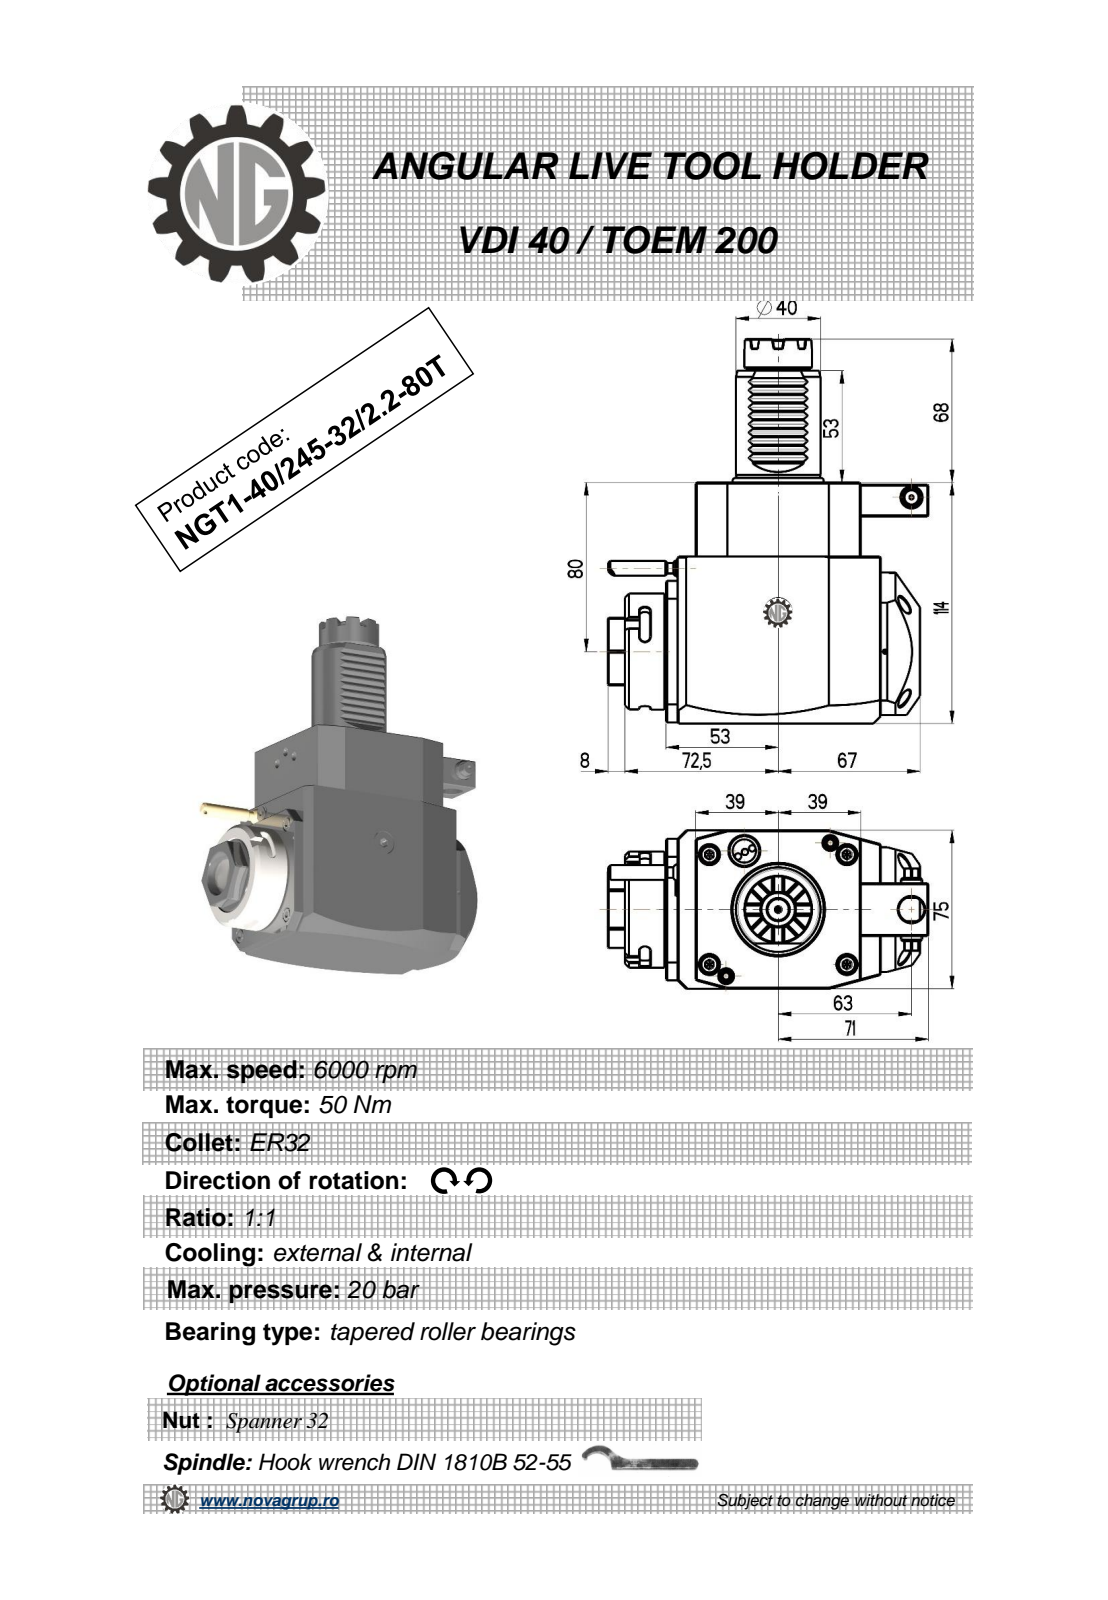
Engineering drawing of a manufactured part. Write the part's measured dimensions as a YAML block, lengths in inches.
part_name: "NGT1_40_245_32_1_2_80T"
step_written_by: "PRO/ENGINEER BY PARAMETRIC TECHNOLOGY CORPORATION, 2010280 (CONFIG_CONTROL_DESIGN)"
units: inches
bodies: {solids: 1, faces: 419, planar: 227, cylindrical: 80, other: 112}
overall_size: [7.165, 5.965, 2.953]
volume: 58.69
surface_area: 113
round_holes:
  - {diameter: 0.079, count: 1}
  - {diameter: 0.098, count: 1}
  - {diameter: 0.118, count: 1}
  - {diameter: 0.374, count: 1}
  - {diameter: 0.472, count: 1}
  - {diameter: 0.906, count: 1}
round_bosses_or_shafts:
  - {diameter: 0.315, count: 2}
  - {diameter: 2.165, count: 1}
  - {diameter: 1.89, count: 1}
  - {diameter: 1.575, count: 1}
  - {diameter: 1.26, count: 1}
  - {diameter: 0.677, count: 1}
  - {diameter: 0.394, count: 1}
  - {diameter: 0.276, count: 1}
partial_cylinders:
  - {radius: 0.012, count: 10}
  - {radius: 0.098, count: 6}
  - {radius: 7.087, count: 2}
  - {radius: 0.02, count: 1}
  - {radius: 0.152, count: 1}
  - {radius: 0.167, count: 1}
  - {radius: 0.965, count: 1}
  - {radius: 1.476, count: 1}
face_to_face_distances: [2.953, 4.488, 0.551, 3.622, 3.071, 0.984, 0.768, 1.319, 4.39, 0.157]
hole_center_spacings: [1.47, 1.701, 2.854]
